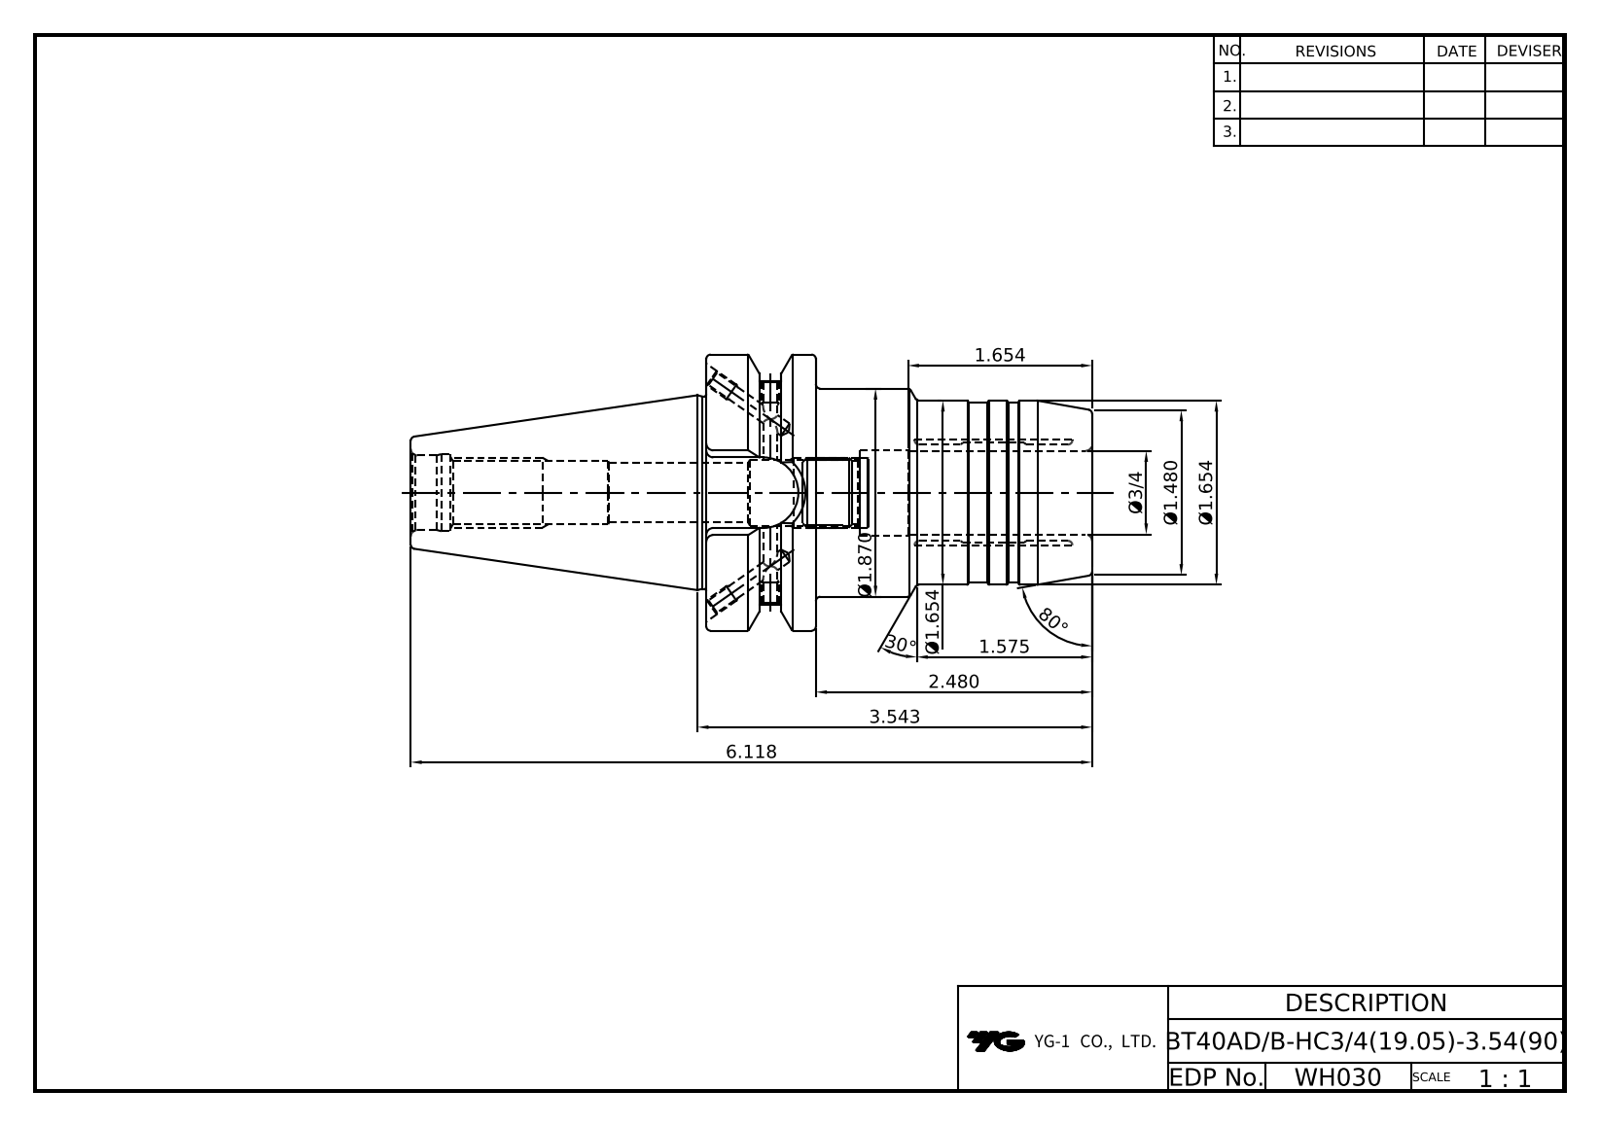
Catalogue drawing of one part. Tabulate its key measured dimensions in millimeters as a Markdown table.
| quantity | value |
| --- | --- |
| part name | BT40ADB-HC19.05-90 |
| STEP written by | Autodesk Inventor 2020 (AUTOMOTIVE_DESIGN) |
| units | millimeters |
| bodies | 1 solid, 90 faces (21 planar, 33 cylindrical, 36 other) |
| overall size | 155.4 × 63 × 63 |
| volume | 194 940 mm³ |
| surface area | 35 154 mm² |
| round holes (diameter × count) | 3.24 × 4, 4 × 4, 13.5 × 1, 13.84 × 1, 14.92 × 1, 17 × 1, 17.6 × 1, 19.05 × 1, 19.4 × 1 |
| round bosses / shafts (diameter × count) | 63 × 1, 51 × 1, 47.5 × 1, 44 × 1, 42 × 1, 41 × 1 |
| partial cylindrical surfaces (radius × count) | 8.05 × 1 |
| main face-to-face distances | 25, 88, 63, 45.2, 17.1, 7.9, 70.9, 12.1, 5, 12.9 |
